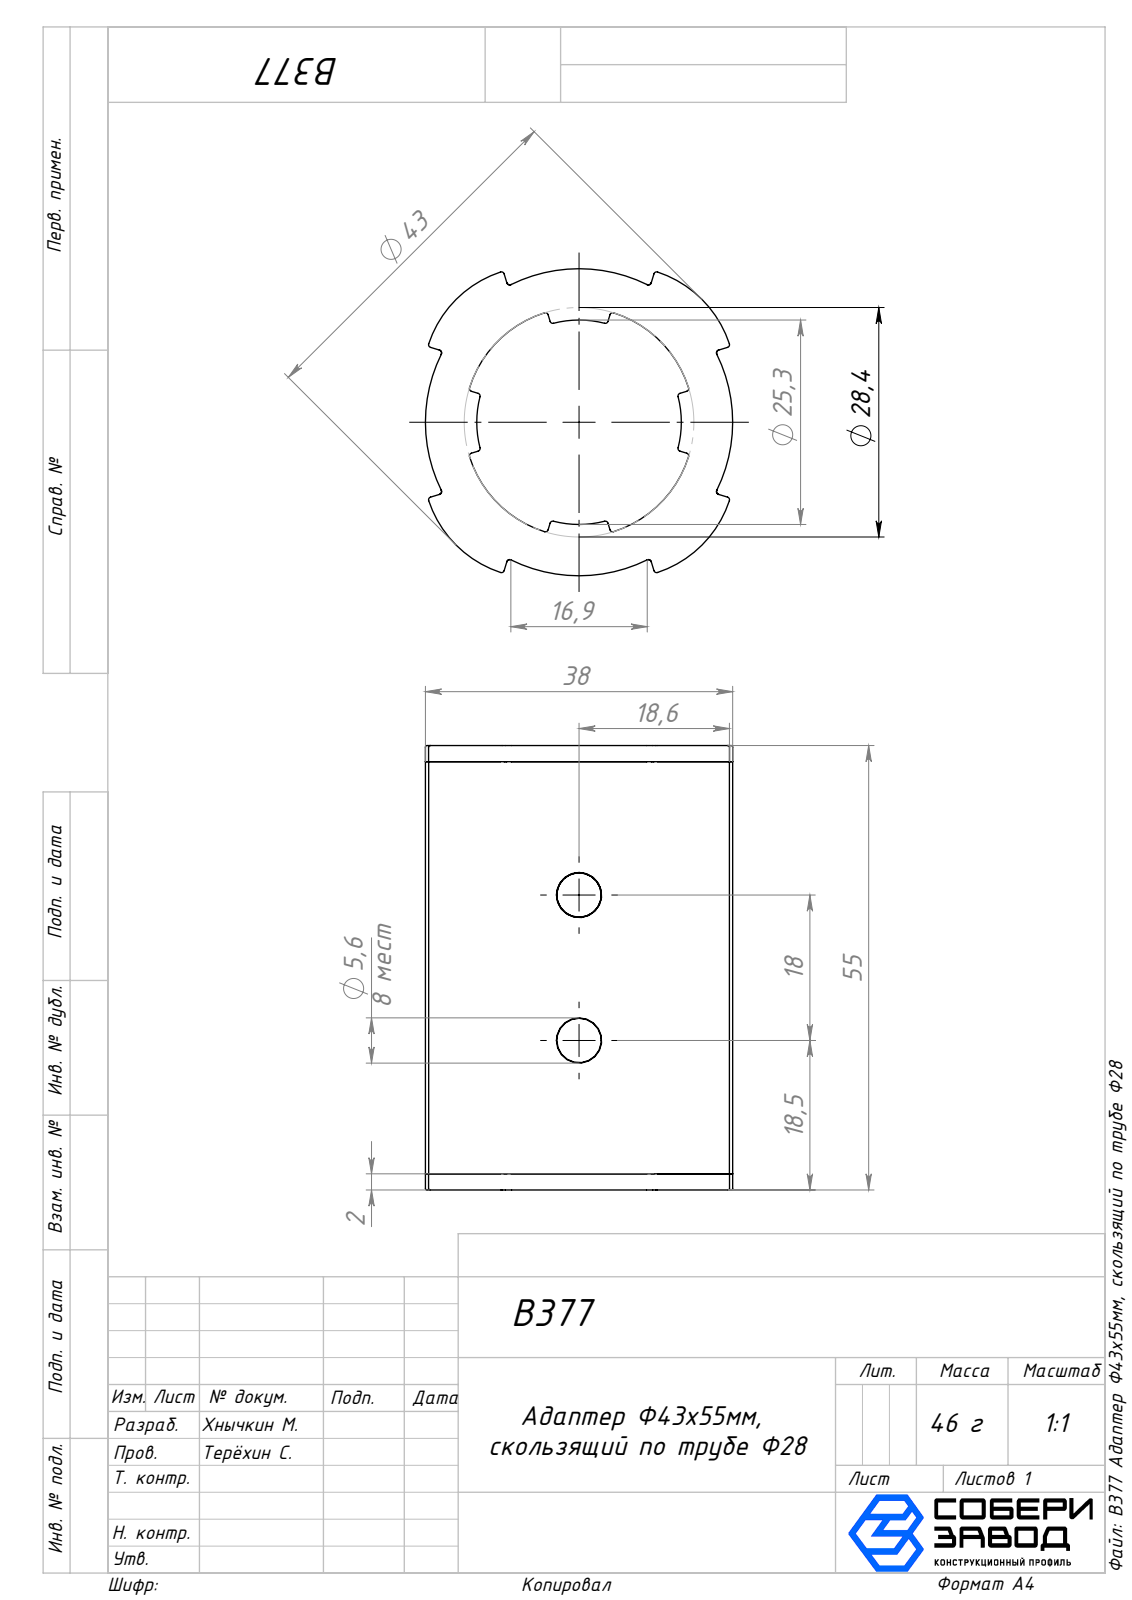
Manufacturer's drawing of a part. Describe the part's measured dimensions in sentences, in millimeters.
The part is named "Корпус_00; B377 Адаптер Ф43х55мм, скользящий по трубе Ф28; Крышка_00". Its 3-D file was written by "SolidWorks 2025 (AUTOMOTIVE_DESIGN)". It is 3 solids with 686 faces: 176 planar, 370 cylindrical and 140 other. Overall it measures 55 by 38 by 38 millimeters. Its volume is 21 923 cubic millimeters and its surface area 23 384 square millimeters. Round holes: 2 of diameter 5.6, 1 of diameter 30. Partial cylindrical surfaces (rounded edges, fillets, slot ends): 40 of radius 0.35, 36 of radius 0.45, 32 of radius 0.2, 16 of radius 0.4, 12 of radius 1, 4 of radius 14, 3 of radius 16.8, 1 of radius 12.65. The main face-to-face distances are 2, 53, 51, 55, 42, 20.59, 13, 11, 40, 9.5. The hole center spacings are 18.
